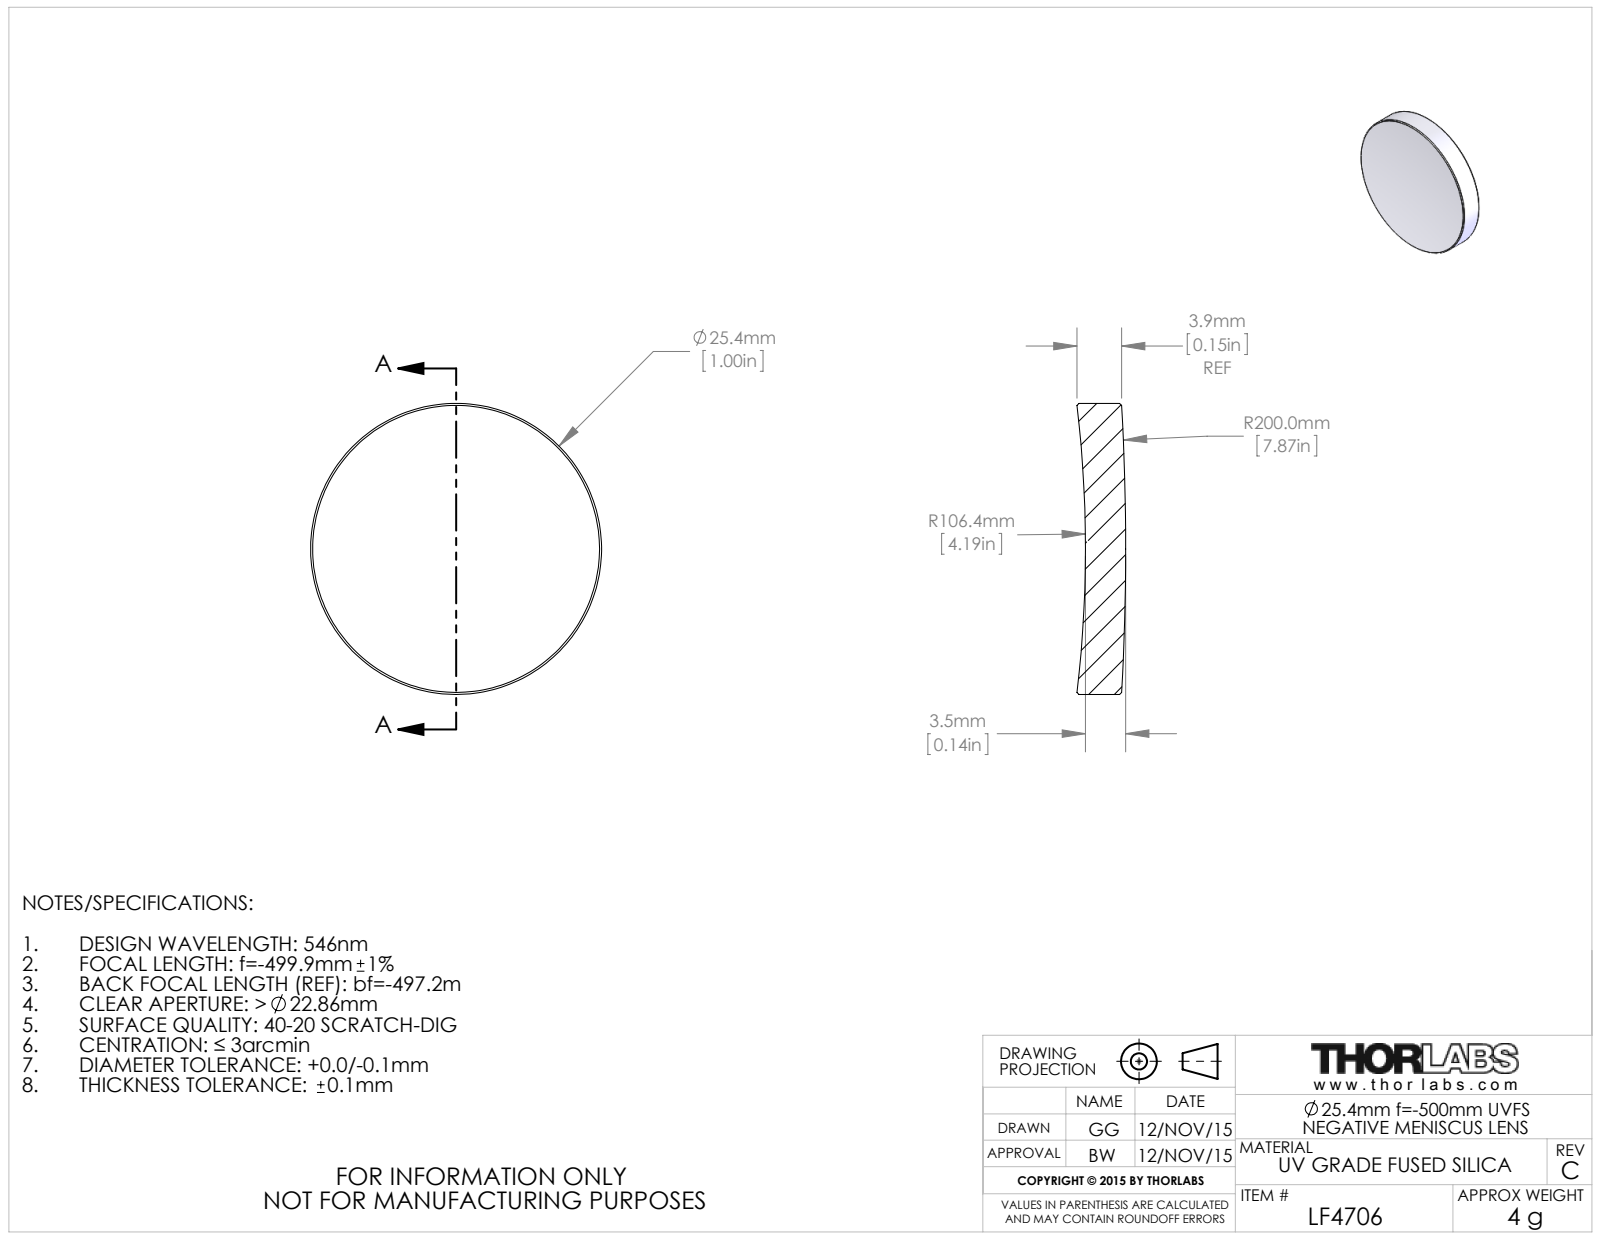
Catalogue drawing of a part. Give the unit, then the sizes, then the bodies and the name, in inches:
Units: inches
Overall size (bounding box): 1 × 1 × 0.167
Round bosses / shafts (diameter × count): ⌀1 ×1
Volume: 0.114 in³ · Surface area: 2.029 in²
Bodies: 1 solid, 10 faces (0 planar, 2 cylindrical, 8 other)
Part name (STEP PRODUCT): 4222-E0W
STEP written by: SolidWorks 2014 (CONFIG_CONTROL_DESIGN)
